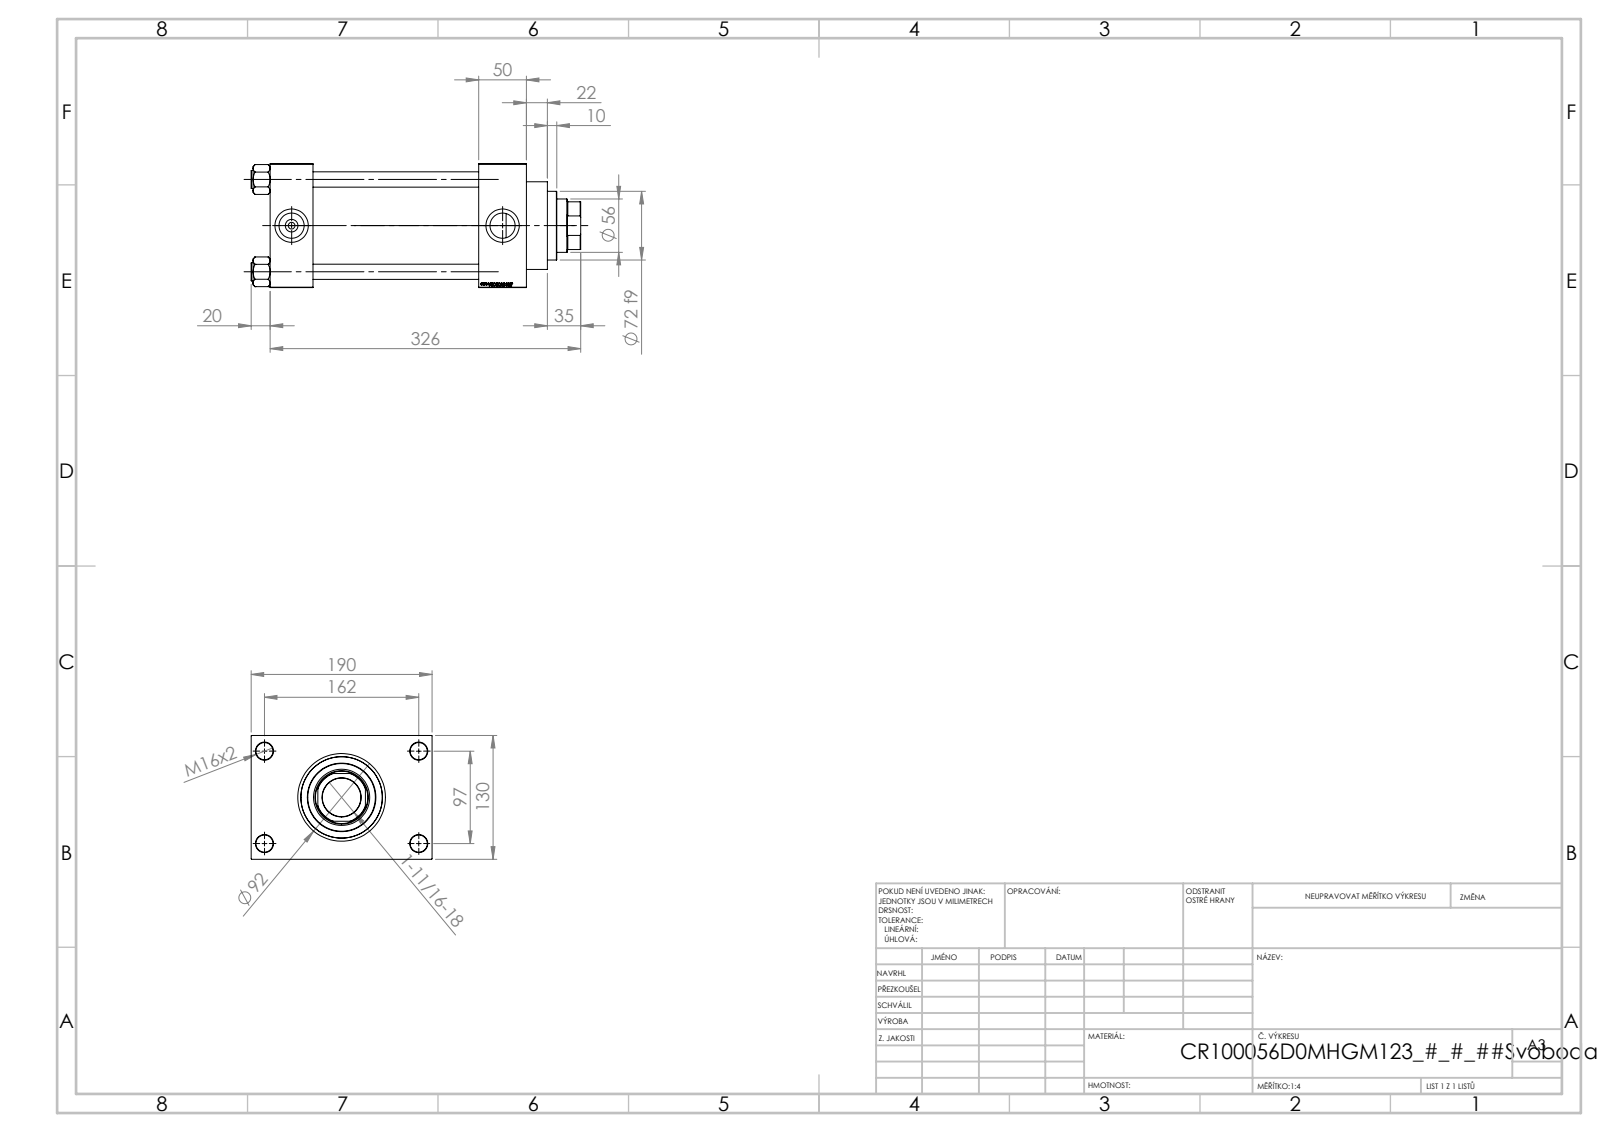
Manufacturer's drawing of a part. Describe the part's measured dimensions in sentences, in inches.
The part is named "V215CR_D_Body; V215_VC_A; NUT_M5_D; V215CR_VCP_D (+1 more)". Its 3-D file was written by "SolidWorks 2019 (CONFIG_CONTROL_DESIGN)". It is 11 solids with 1151 faces: 545 planar, 88 cylindrical and 518 other. Overall it measures 13.622 by 7.48 by 5.118 inches. Its volume is 187 cubic inches and its surface area 725.2 square inches. Round holes: 4 of diameter 0.63, 4 of diameter 0.709, 2 of diameter 0.276, 2 of diameter 1.041, 2 of diameter 1.378, 1 of diameter 1.594, 1 of diameter 2.205, 1 of diameter 2.323, 1 of diameter 2.992, 1 of diameter 3.366, 1 of diameter 3.937. Round bosses or shafts: 4 of diameter 0.748, 1 of diameter 4.173, 1 of diameter 3.622, 1 of diameter 2.835. Partial cylindrical surfaces (rounded edges, fillets, slot ends): 1 of radius 1.063. The main face-to-face distances are 5.118, 1.969, 1.772, 8.622, 6.85, 10.591, 8.819, 1.181, 6.299, 7.48. The hole center spacings are 1.281, 2.698, 3.717, 3.815, 4.026, 5.096, 6.367, 3.819.
